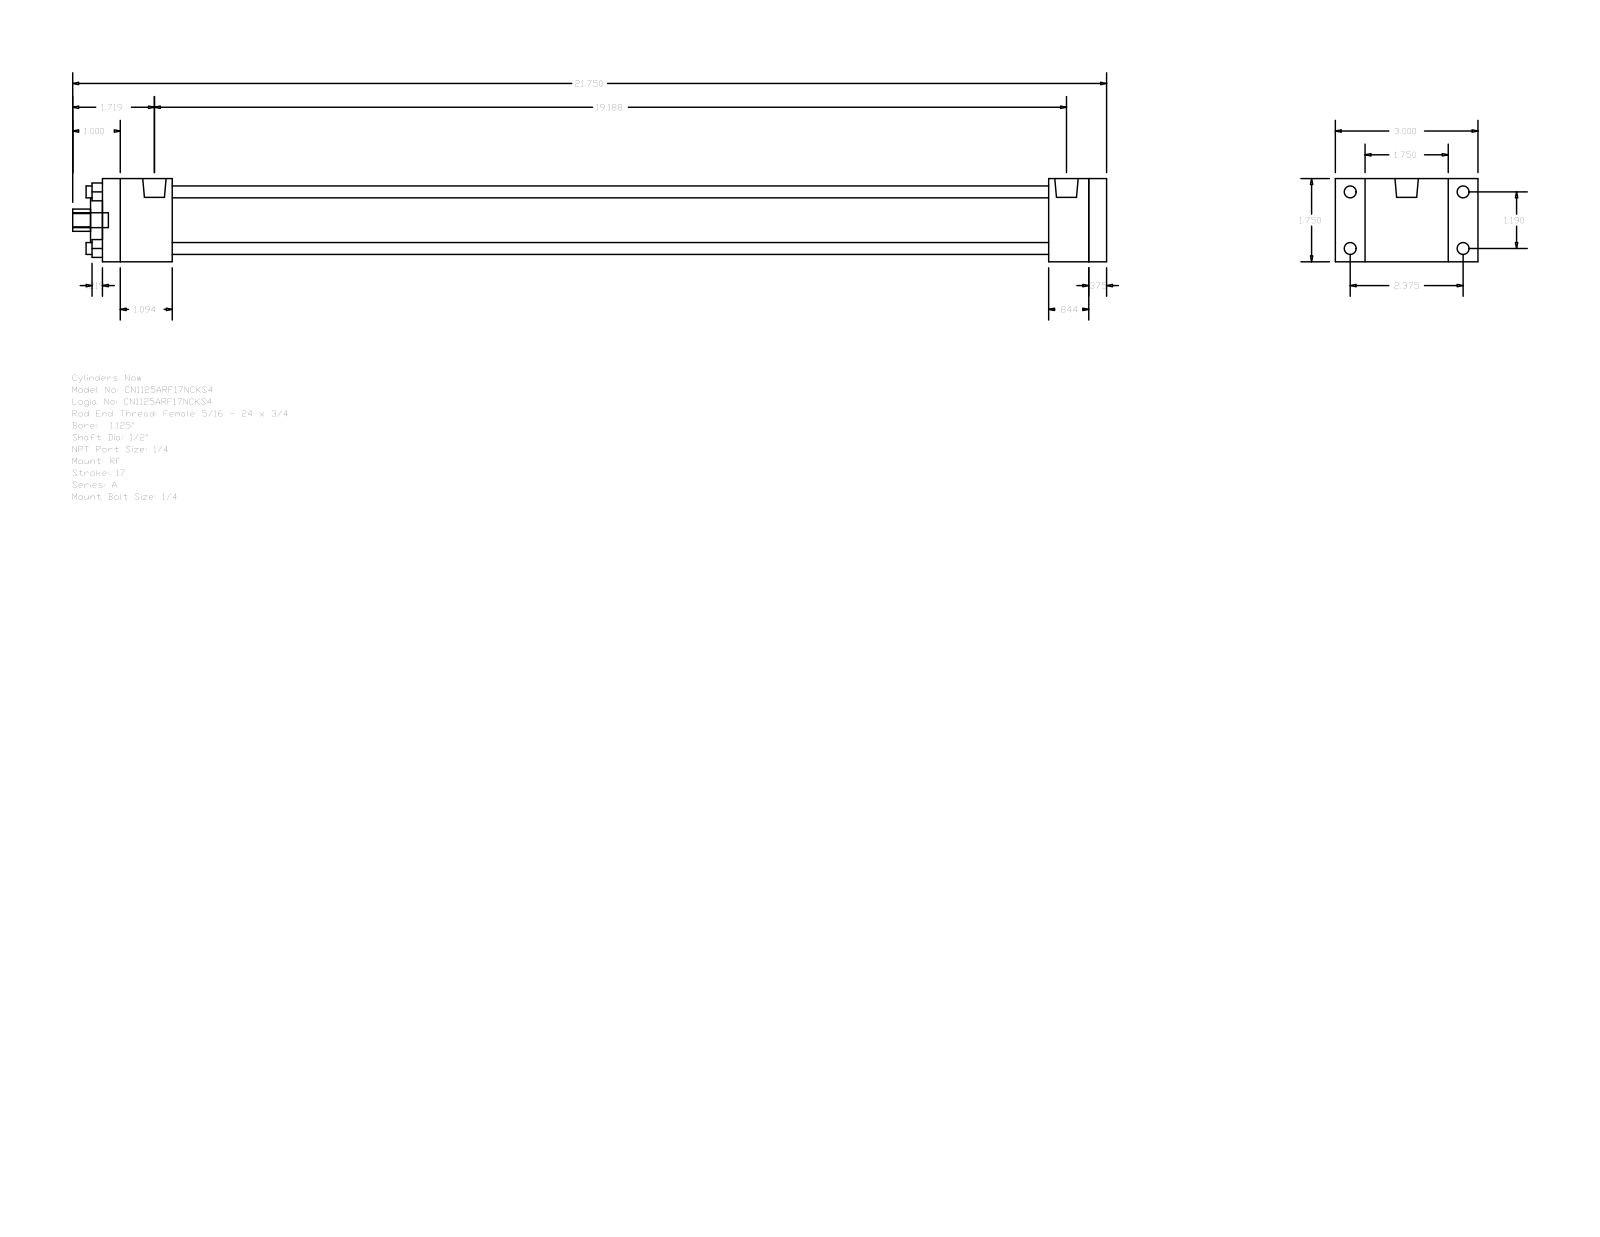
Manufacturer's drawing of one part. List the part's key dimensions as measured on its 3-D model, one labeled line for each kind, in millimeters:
Part name (STEP PRODUCT): A_RF__0112_0.5
STEP written by: GSSL Pune (CONFIG_CONTROL_DESIGN)
Units: millimetres
Bodies: 0 solids, 92 faces (64 planar, 28 cylindrical, 0 other)
Overall size (bounding box): 552.45 × 76.2 × 44.45
Round holes (diameter × count): ⌀6.35 ×4, ⌀12.7 ×1, ⌀23.81 ×1, ⌀31.88 ×1
Round bosses / shafts (diameter × count): ⌀6.35 ×4, ⌀5.56 ×4, ⌀12.49 ×2, ⌀7.94 ×1
Partial cylindrical surfaces — rounded edges, fillets, slot ends (radius × count): R5.94 ×1
Main face-to-face distances: 44.46, 9.53, 536.57, 527.04, 37.3, 505.61, 468.31, 489.74, 499.27, 21.43
Hole centre spacings: 21.37, 30.22, 42.74
